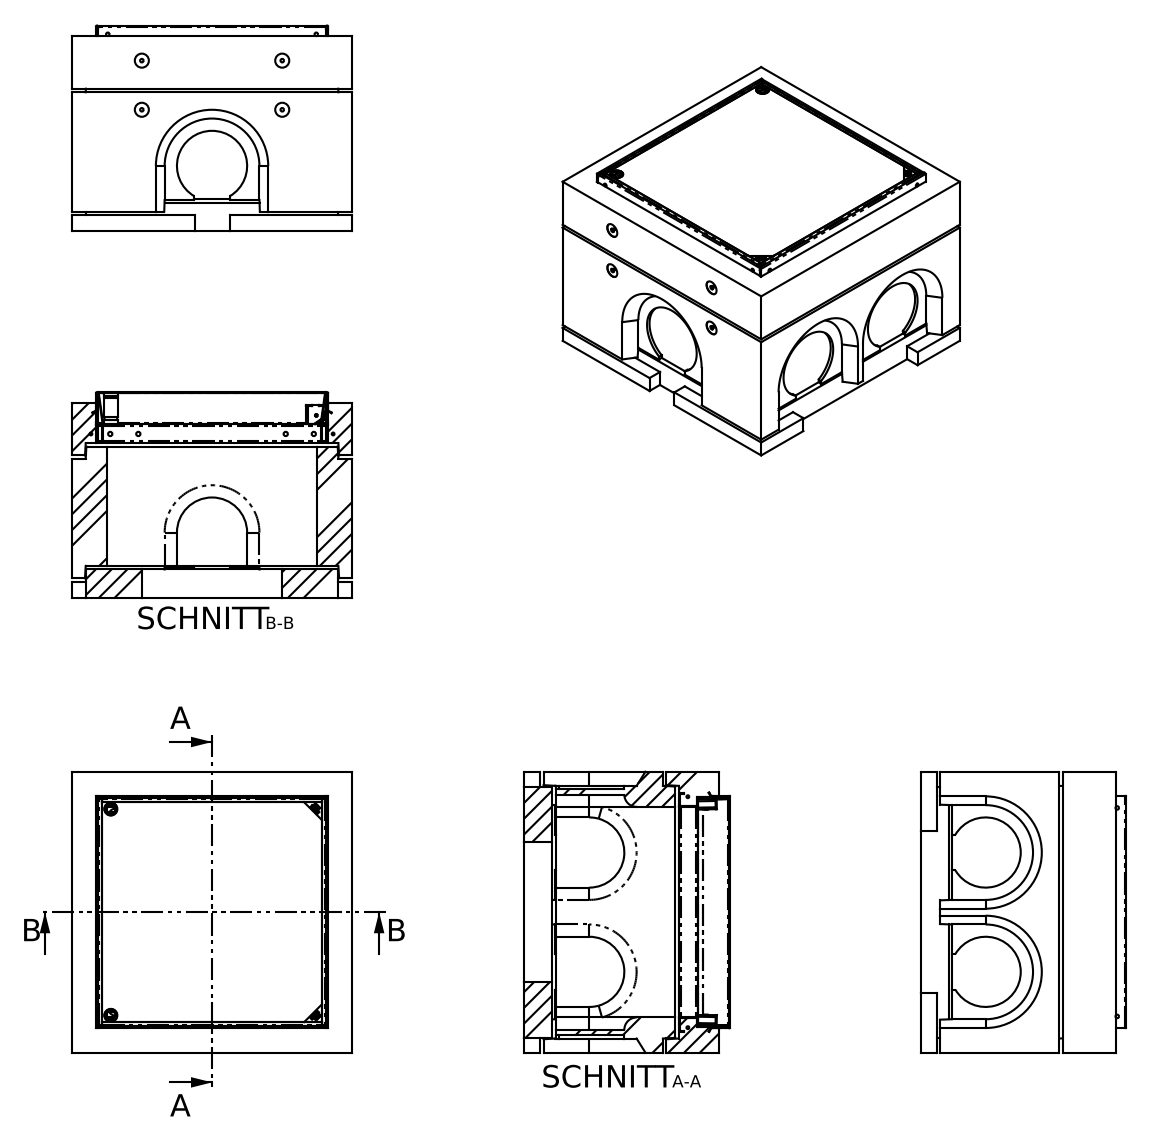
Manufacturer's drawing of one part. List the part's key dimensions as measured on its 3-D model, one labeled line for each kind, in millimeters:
Part name (STEP PRODUCT): SC-ECO.0606.52.B125
STEP written by: SolidWorks 2018 (AUTOMOTIVE_DESIGN)
Units: millimetres
Bodies: 0 solids, 341 faces (194 planar, 92 cylindrical, 55 other)
Overall size (bounding box): 800 × 800 × 585
Round holes (diameter × count): ⌀10 ×4, ⌀200 ×3, ⌀12.2 ×2, ⌀26.5 ×2, ⌀34 ×2, ⌀35 ×2, ⌀40 ×2
Round bosses / shafts (diameter × count): ⌀10 ×4, ⌀5.81 ×4, ⌀50 ×2
Partial cylindrical surfaces — rounded edges, fillets, slot ends (radius × count): R35 ×12, R4 ×8, R2.5 ×4, R3 ×4, R5 ×4, R13.5 ×2
Main face-to-face distances: 100, 700, 25, 800, 10, 35, 90, 494, 1.5, 685
Hole centre spacings: 94.26, 150.8, 235.87, 256.12, 395.92, 403.81, 478.37, 504.72
